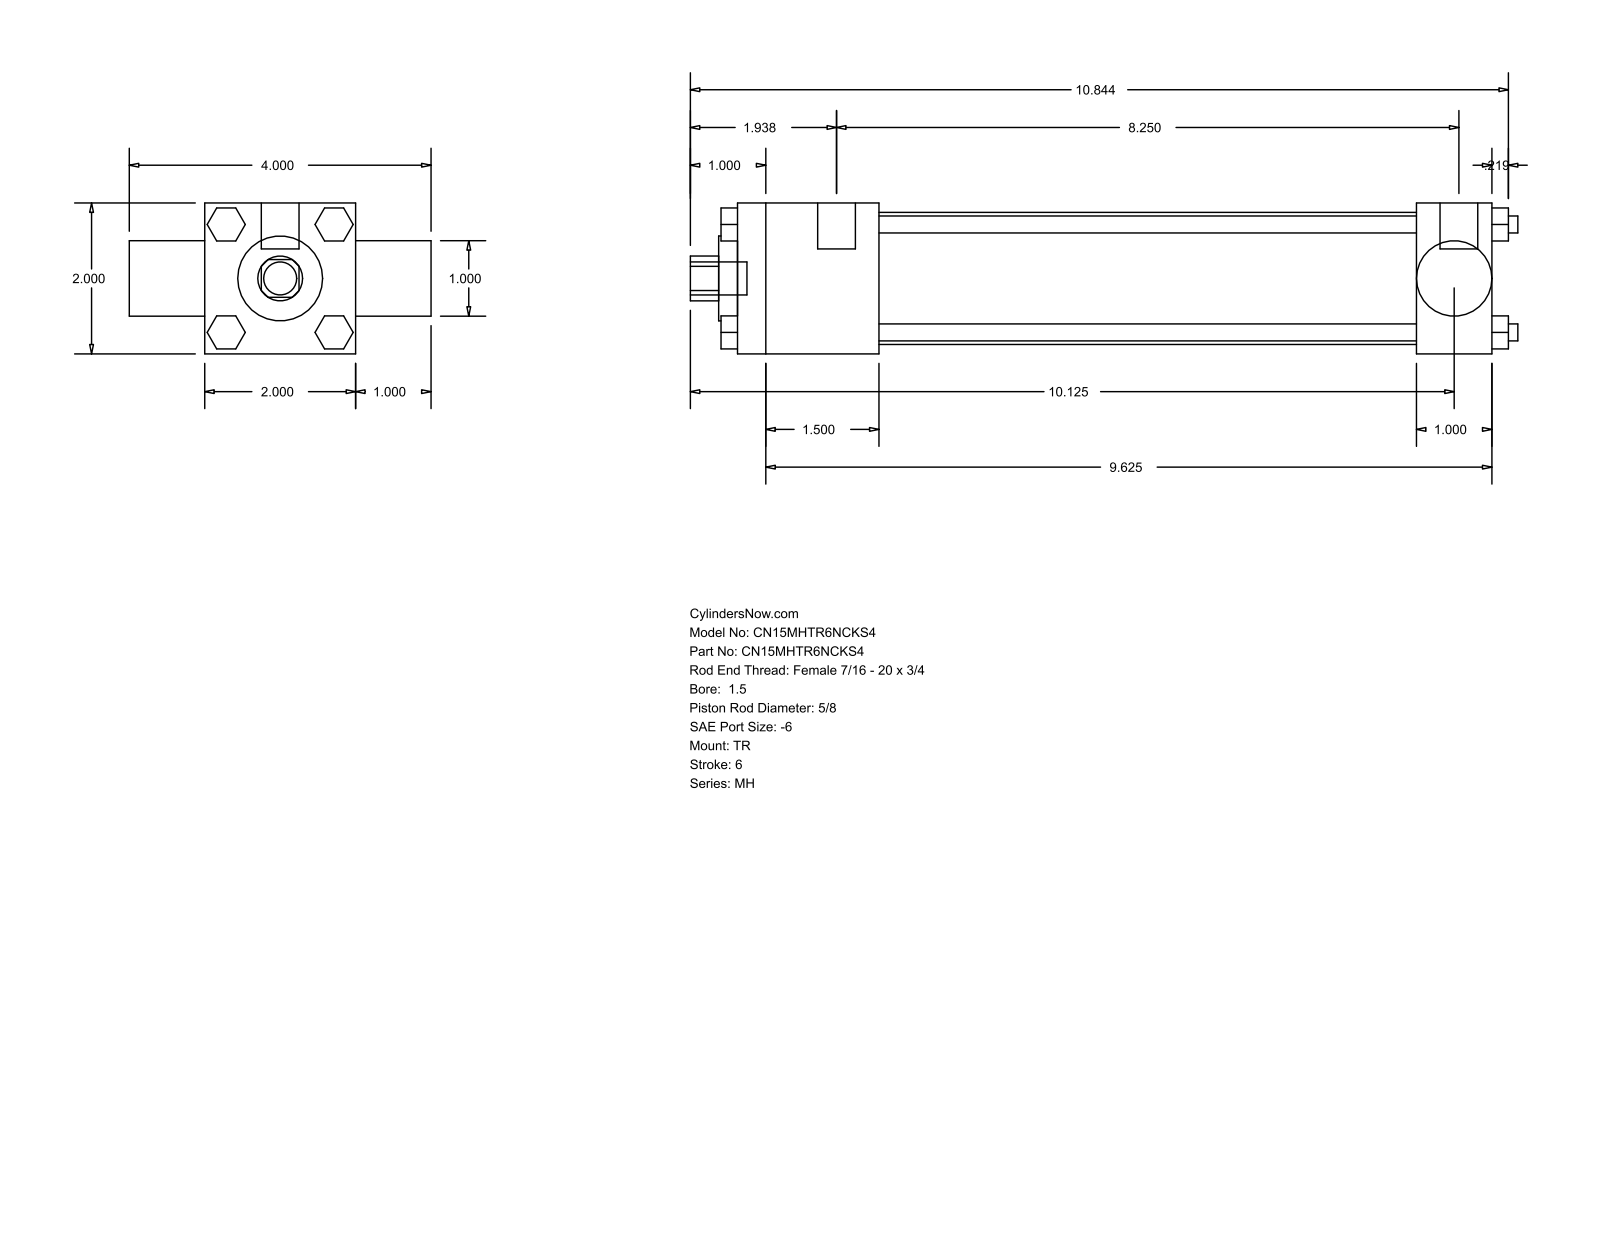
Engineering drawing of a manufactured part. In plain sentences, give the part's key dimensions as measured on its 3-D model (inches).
The part is named "MH_TR__0150_0.625". Its 3-D file was written by "GSSL Pune (CONFIG_CONTROL_DESIGN)". It is 0 solids with 120 faces: 92 planar, 28 cylindrical and 0 other. Overall it measures 10.969 by 4 by 2 inches. Round holes: 1 of diameter 0.625, 1 of diameter 0.998, 1 of diameter 1.125, 1 of diameter 1.75. Round bosses or shafts: 4 of diameter 0.225, 3 of diameter 0.219, 2 of diameter 0.5, 1 of diameter 0.437. Partial cylindrical surfaces (rounded edges, fillets, slot ends): 1 of radius 0.297. The main face-to-face distances are 2, 10, 1, 3, 1.875, 8.125, 9, 7.125, 1, 0.437.
